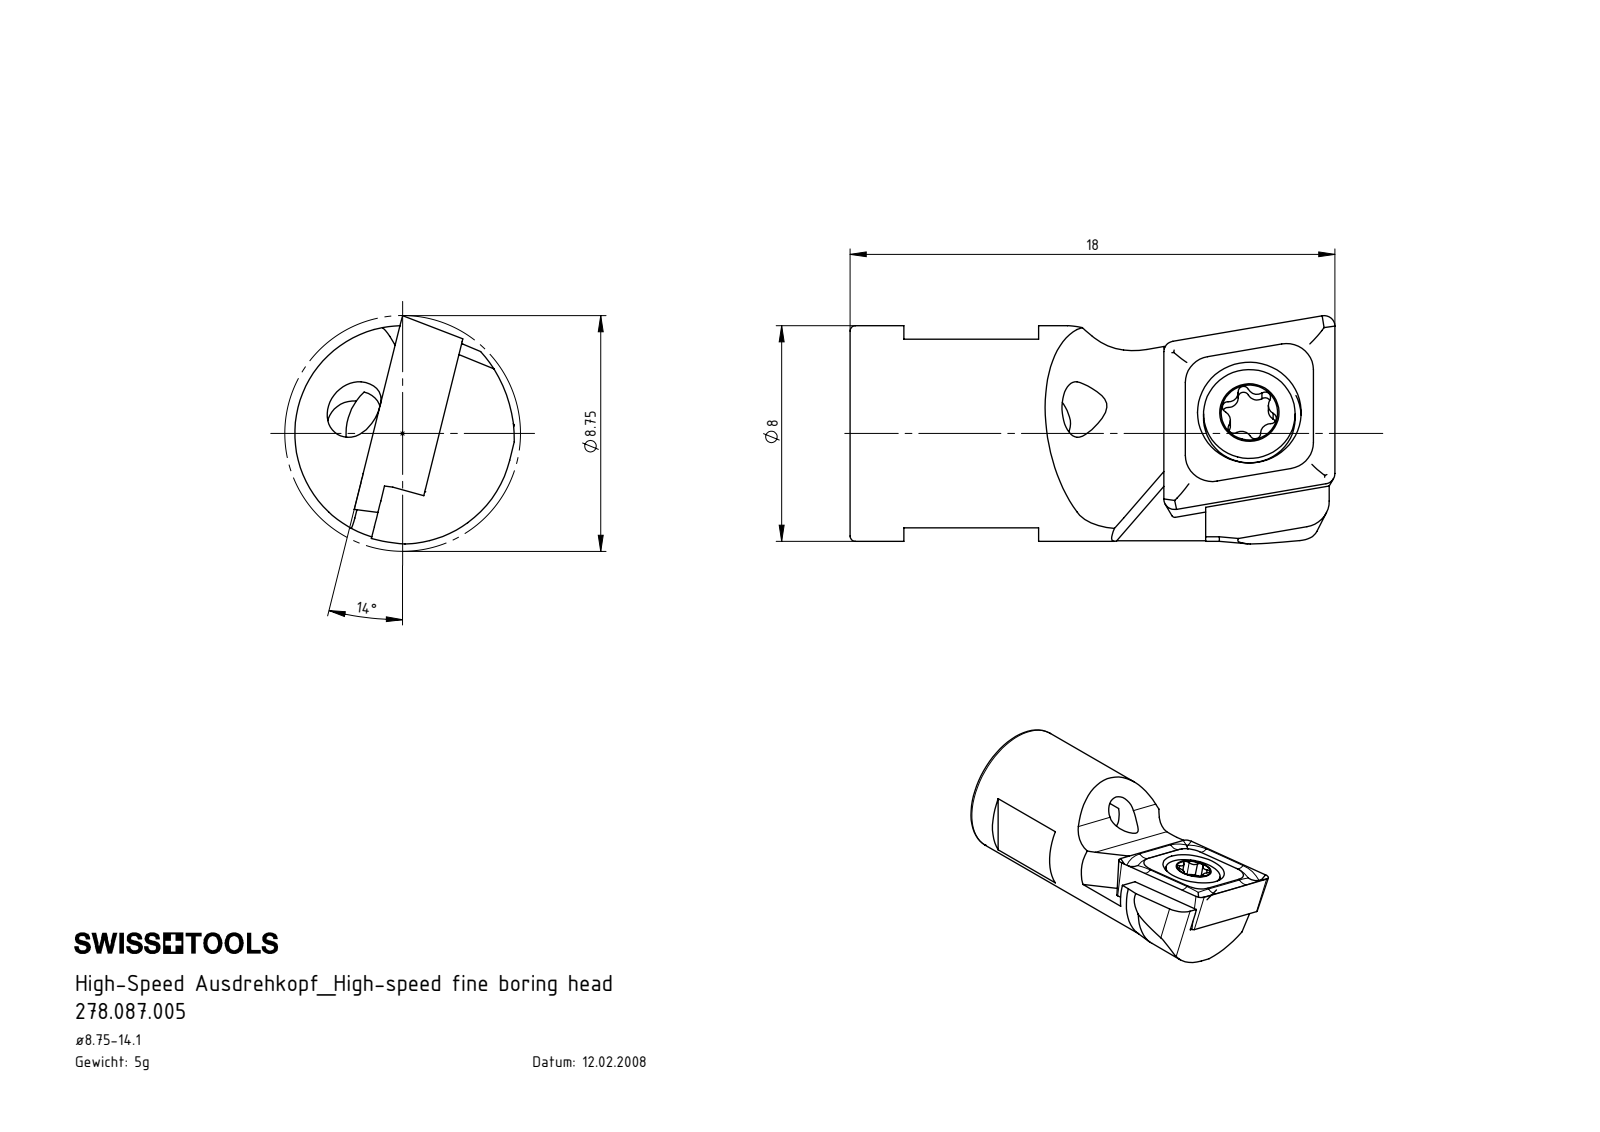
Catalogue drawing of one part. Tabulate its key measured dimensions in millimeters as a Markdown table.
| quantity | value |
| --- | --- |
| part name | HS5-A09.K11.018; HS5-A09.K11.018_C; WCA-ER2.001.005_A; CCMT060204 |
| STEP written by | SolidWorks 2017 (CONFIG_CONTROL_DESIGN) |
| units | millimeters |
| bodies | 3 solids, 128 faces (41 planar, 38 cylindrical, 49 other) |
| overall size | 18 × 8.45 × 8.35 |
| volume | 551 mm³ |
| surface area | 789 mm² |
| round holes (diameter × count) | 2 × 1, 2.05 × 1, 2.8 × 1, 3.85 × 1, 4.2 × 1 |
| round bosses / shafts (diameter × count) | 8 × 1, 3.4 × 1, 2.5 × 1 |
| partial cylindrical surfaces (radius × count) | 0.21 × 6, 0.36 × 5, 0.36 × 1, 1 × 1, 2 × 1, 3 × 1, 4.1 × 1, 4.9 × 1 |
| main face-to-face distances | 7, 2.38, 2.28, 1.5, 0.78, 0.88, 11.8, 5, 4.8, 2 |
